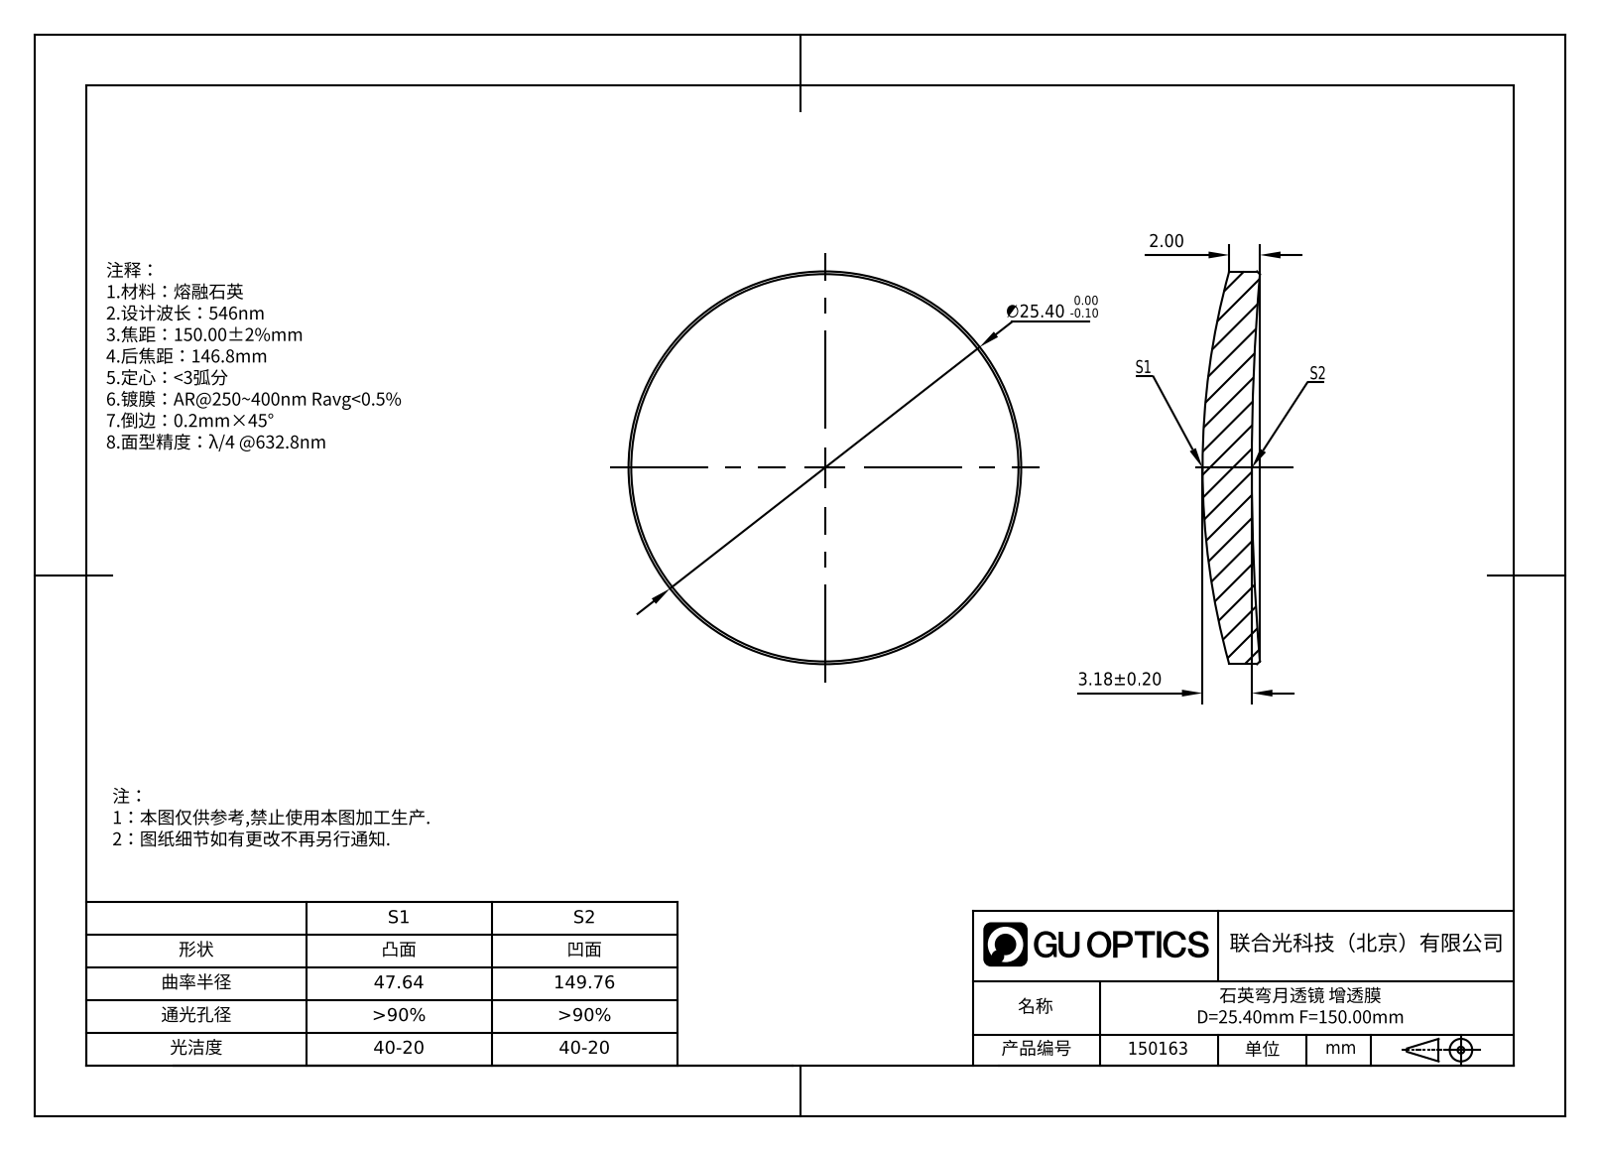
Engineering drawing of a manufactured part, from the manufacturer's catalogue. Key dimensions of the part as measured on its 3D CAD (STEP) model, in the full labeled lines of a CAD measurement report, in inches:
Part name (STEP PRODUCT): GLM2-025B-150-UV
STEP written by: SolidWorks 2022 (AUTOMOTIVE_DESIGN)
Units: inches
Bodies: 1 solid, 8 faces (0 planar, 2 cylindrical, 6 other)
Overall size (bounding box): 1 × 1 × 0.146
Volume: 0.08 in³ · Surface area: 1.818 in²
Round bosses / shafts (diameter × count): ⌀1 ×1
